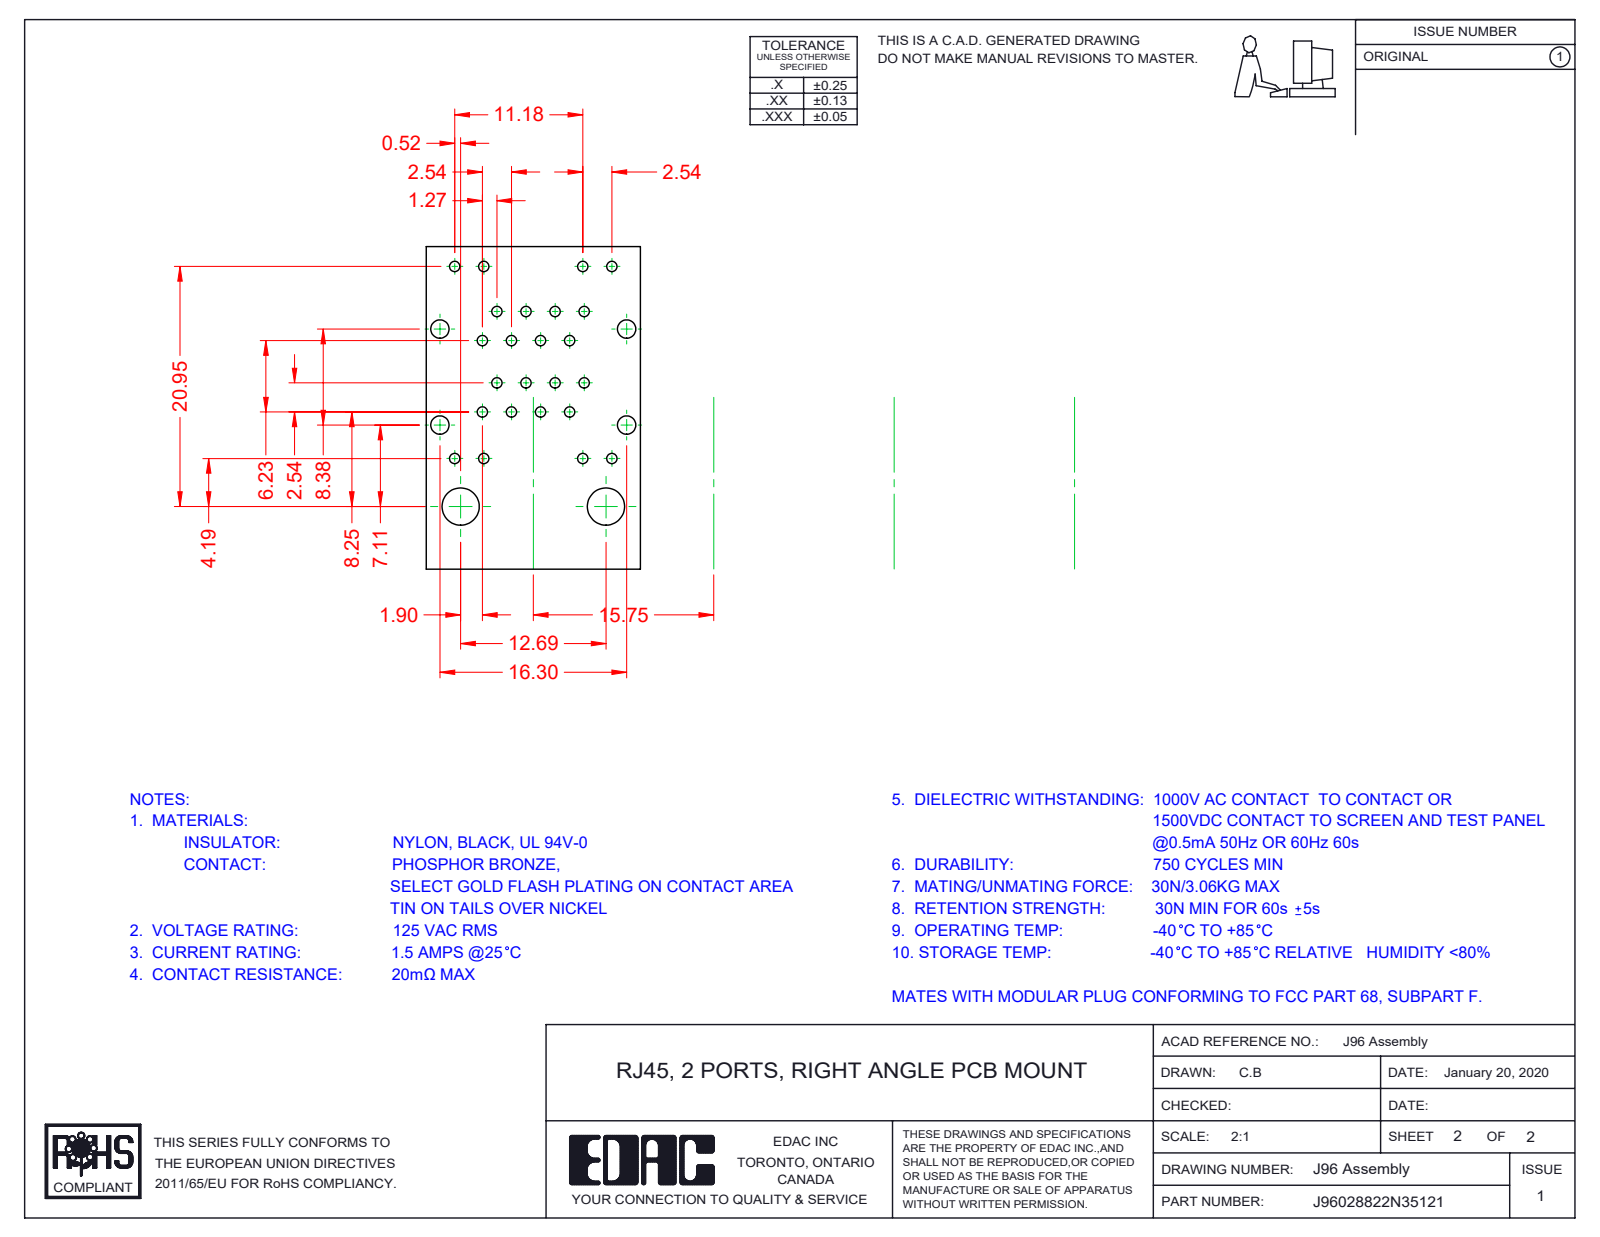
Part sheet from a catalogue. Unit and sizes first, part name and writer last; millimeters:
Units: millimetres
Overall size (bounding box): 29.58 × 28.68 × 16.8
Partial cylindrical surfaces — rounded edges, fillets, slot ends (radius × count): R0.25 ×48, R0.15 ×32, R0.35 ×24, R0.5 ×16, R1 ×16, R0.2 ×13, R0.7 ×9, R2 ×5
Main face-to-face distances: 16.3, 16.1, 1.75, 16.5, 14.75, 1.55, 14.55, 0.53, 1.48, 11.2
Volume: 6 852 mm³ · Surface area: 19 109 mm²
Bodies: 27 solids, 2386 faces (1849 planar, 431 cylindrical, 106 other)
Part name (STEP PRODUCT): 96 Grounding_2 Ports; 96 LED LH Lower_3-Green; 96 LED RH Upper_5-Green-Yellow; 96 Shield_2 Ports LED - No EMI (+8 more)
STEP written by: SolidWorks 2016 (CONFIG_CONTROL_DESIGN)
